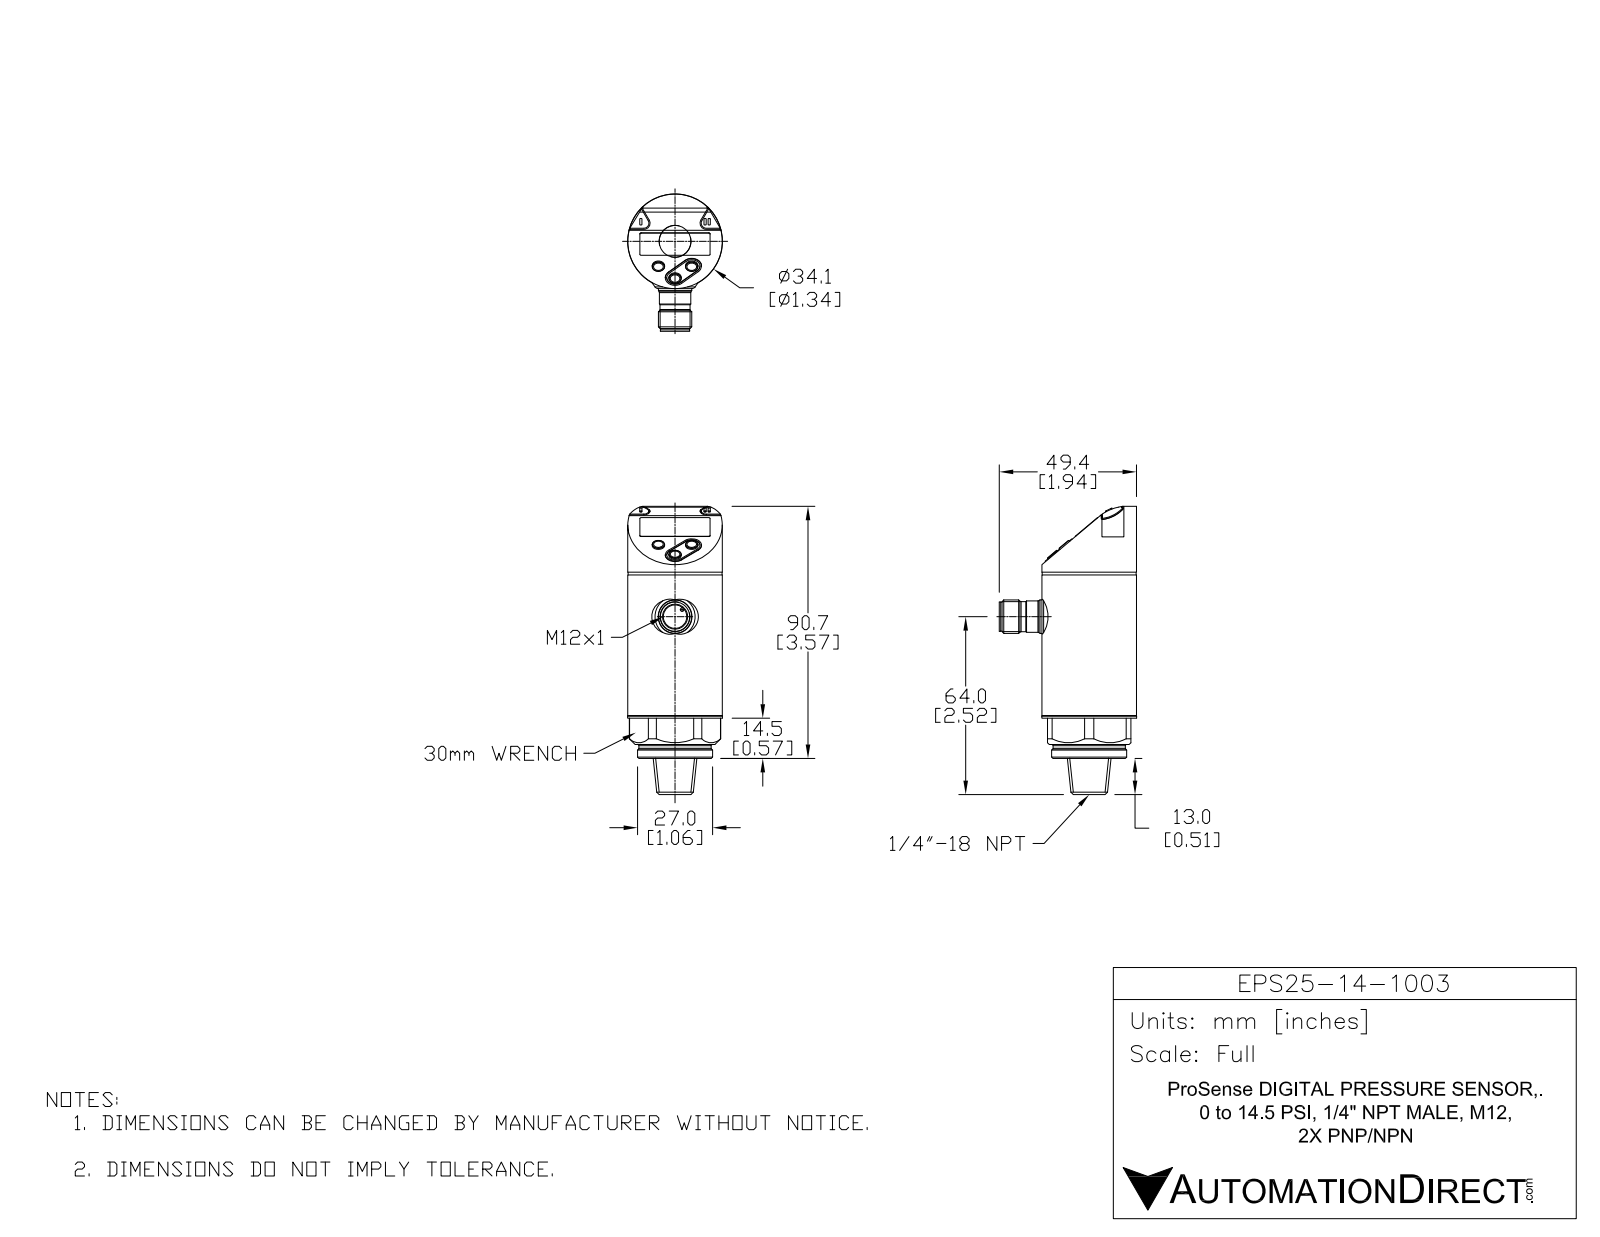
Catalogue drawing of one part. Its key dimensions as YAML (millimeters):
part_name: "EPS25-14-1003"
step_written_by: "SolidWorks 2016 (AUTOMOTIVE_DESIGN)"
units: millimeters
bodies: {solids: 11, faces: 370, planar: 207, cylindrical: 84, other: 79}
overall_size: [103.7, 49.4, 34.1]
volume: 72203
surface_area: 21365
round_holes:
  - {diameter: 4.2, count: 1}
  - {diameter: 8.45, count: 1}
round_bosses_or_shafts:
  - {diameter: 1.4, count: 4}
  - {diameter: 1, count: 4}
  - {diameter: 34.1, count: 1}
  - {diameter: 34, count: 1}
  - {diameter: 33.8, count: 1}
  - {diameter: 27, count: 1}
  - {diameter: 26, count: 1}
  - {diameter: 12, count: 1}
partial_cylinders:
  - {radius: 1.8, count: 2}
  - {radius: 2.2, count: 2}
  - {radius: 3, count: 2}
  - {radius: 3.5, count: 2}
  - {radius: 15, count: 2}
  - {radius: 0.61, count: 1}
  - {radius: 6.8, count: 1}
  - {radius: 16.44, count: 1}
face_to_face_distances: [0.68, 11.5, 12.18, 10.68, 1.5, 10, 2, 2.5, 14, 4]
